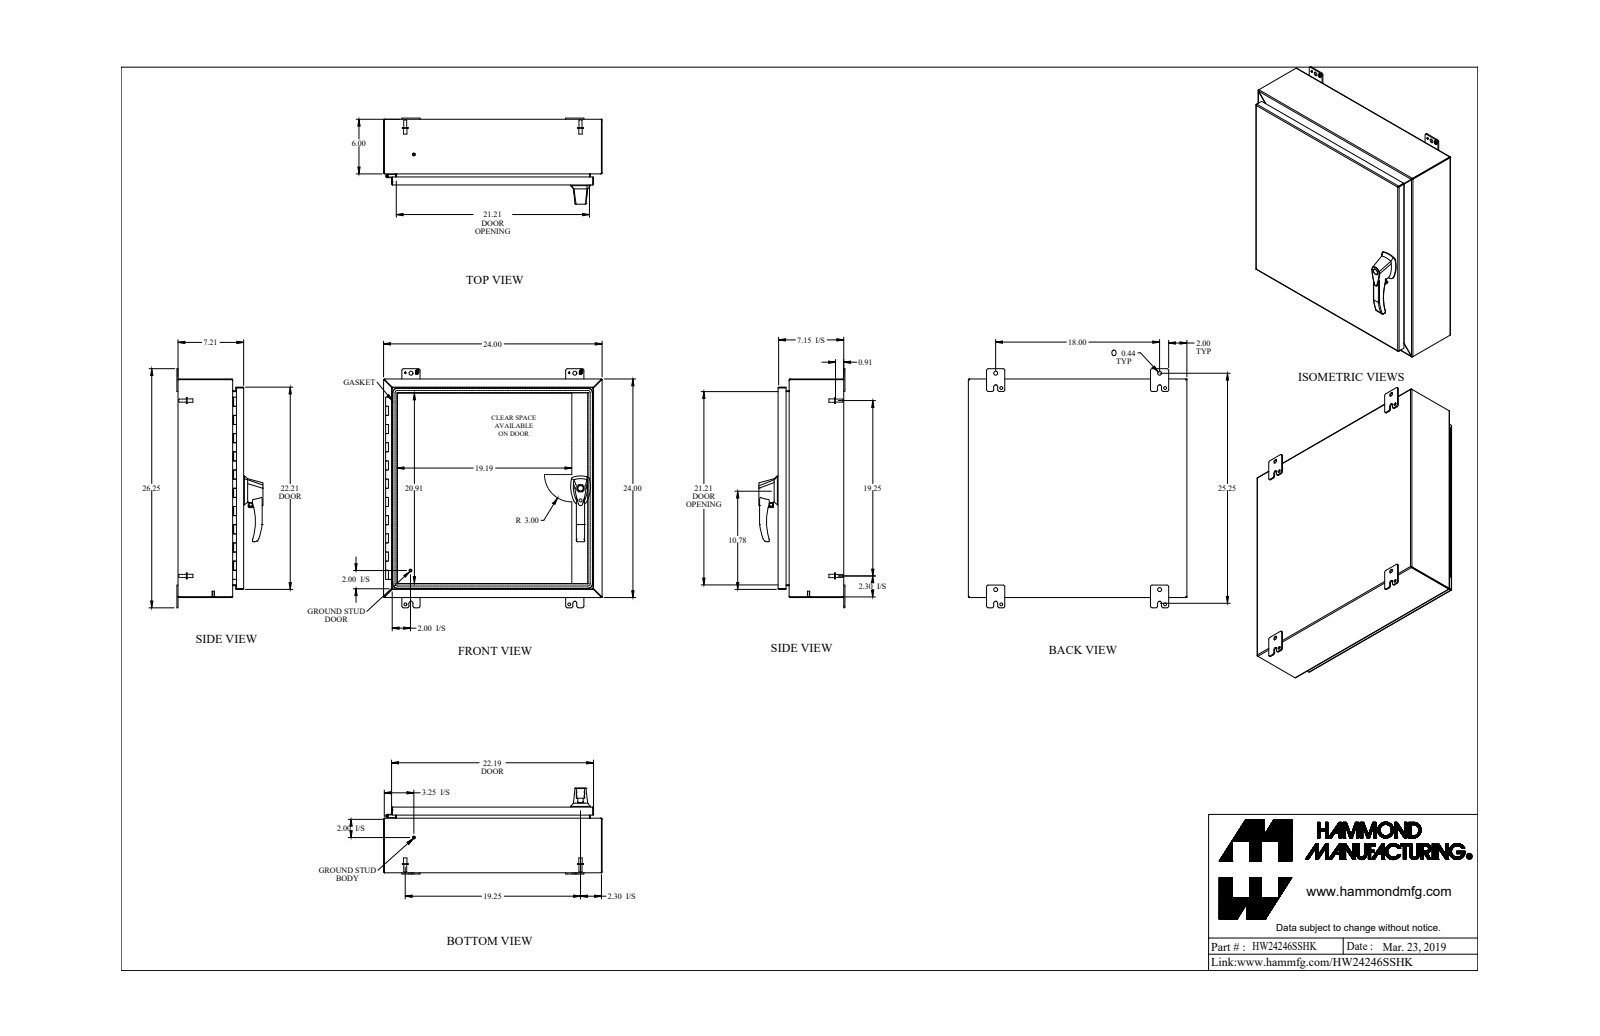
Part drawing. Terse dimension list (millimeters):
name: HW24246SSHK
written by: SolidWorks 2018 (AUTOMOTIVE_DESIGN)
unit: mm
bodies: 46 solids, 1423 faces (699 planar, 569 cylindrical, 155 other)
size: 666.8 × 609.6 × 240
volume: 2 830 000 mm³; area: 2 850 000 mm²
holes: 6× ⌀4.5, 5× ⌀8, 3× ⌀6.4, 3× ⌀6.7, 3× ⌀10.5, 2× ⌀5, 2× ⌀6.5, 2× ⌀10, 2× ⌀11.1, 1× ⌀4.7, 1× ⌀5.9, 1× ⌀8.4
bosses: 9× ⌀9.5, 7× ⌀6.4, 6× ⌀4, 4× ⌀16.5, 4× ⌀8.4, 3× ⌀25.4, 3× ⌀13, 2× ⌀16
rounds: 27× R6.4, 24× R4.8, 20× R0.9, 20× R2.7, 12× R1.5, 9× R3.2, 8× R1.1, 8× R5.5
face distances: 1.8, 1.8, 607.8, 181.3, 179.5, 181.3, 183.1, 605.9, 609.6, 150.6
hole spacings: 28.2, 206.2, 206.2, 412.4, 206.2, 457.2, 558.3, 25.5
